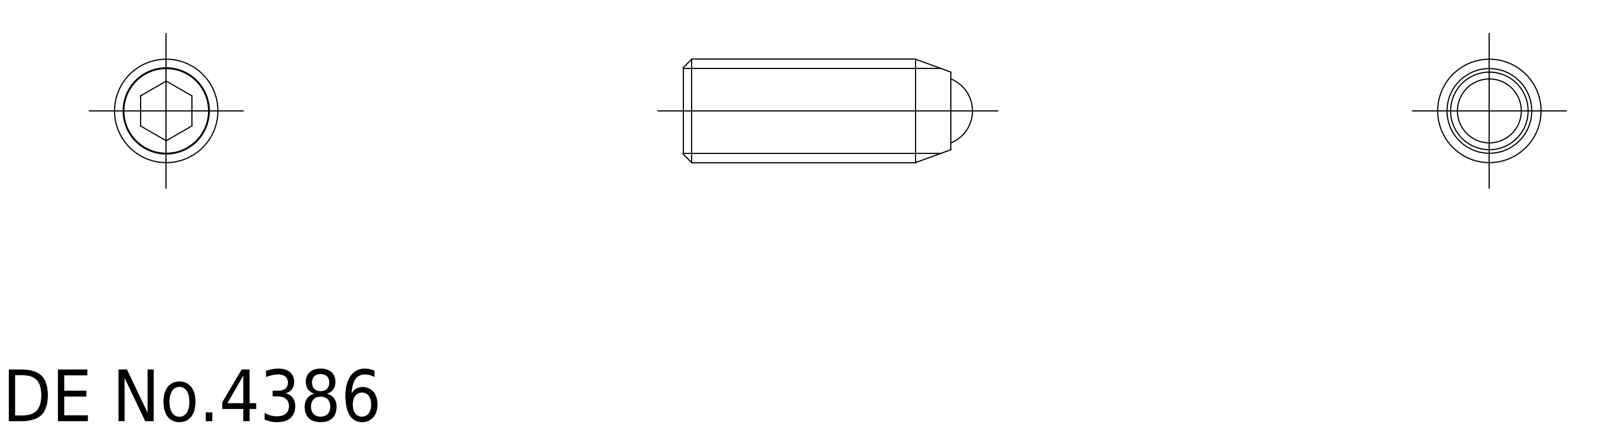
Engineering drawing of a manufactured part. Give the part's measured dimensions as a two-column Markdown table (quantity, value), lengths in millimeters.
| quantity | value |
| --- | --- |
| part name | ball; SCS_M6_16_R_17401_36 |
| STEP written by | CADfix (AUTOMOTIVE_DESIGN) |
| units | millimeters |
| bodies | 2 solids, 20 faces (0 planar, 0 cylindrical, 20 other) |
| overall size | 16.8 × 6 × 6 |
| volume | 373 mm³ |
| surface area | 476 mm² |
